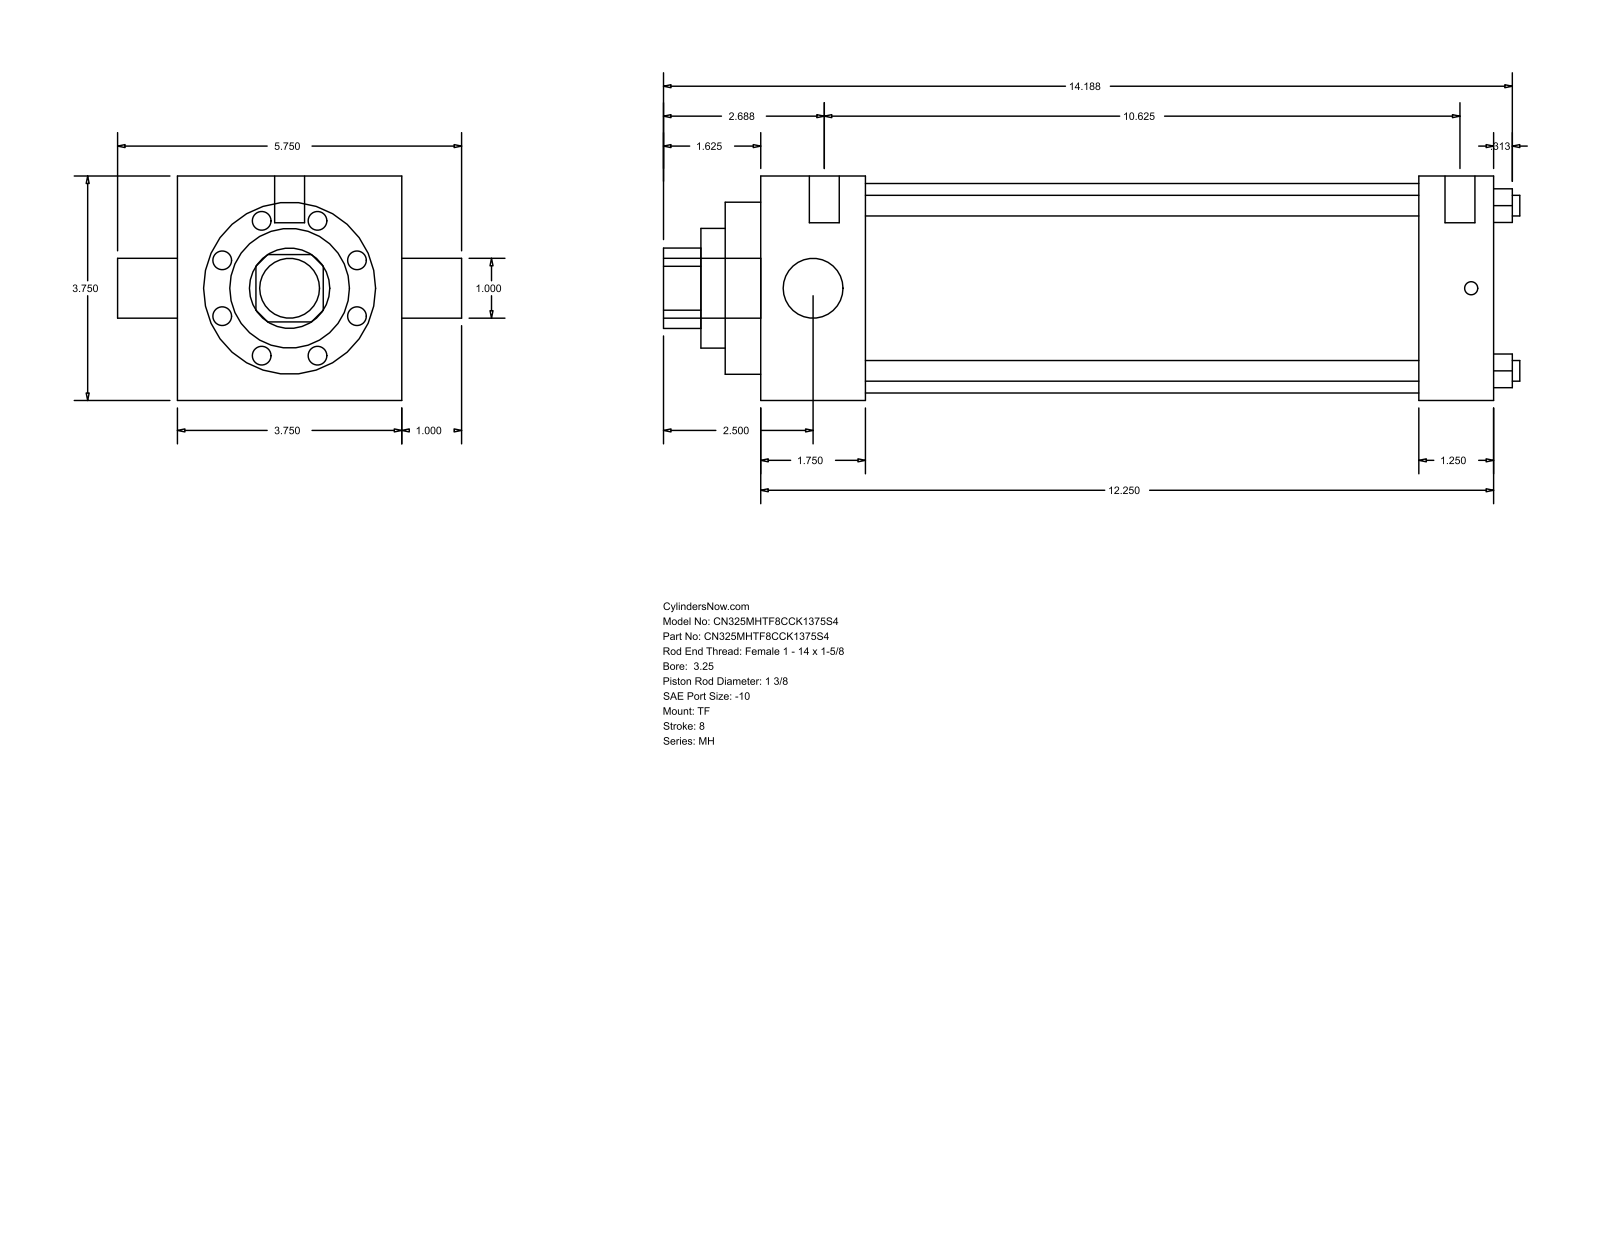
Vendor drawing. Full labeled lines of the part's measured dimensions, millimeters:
Part name (STEP PRODUCT): MH_TF__0325_1.375
STEP written by: GSSL Pune (CONFIG_CONTROL_DESIGN)
Units: millimetres
Bodies: 0 solids, 86 faces (61 planar, 25 cylindrical, 0 other)
Overall size (bounding box): 363.54 × 146.05 × 95.25
Round holes (diameter × count): ⌀8.76 ×4, ⌀25.4 ×1, ⌀34.92 ×1, ⌀50.8 ×1, ⌀73.03 ×1, ⌀88.9 ×1
Round bosses / shafts (diameter × count): ⌀5.56 ×3, ⌀12.7 ×2, ⌀25.4 ×1
Partial cylindrical surfaces — rounded edges, fillets, slot ends (radius × count): R17.06 ×1
Main face-to-face distances: 95.24, 311.16, 44.45, 279.41, 234.96, 266.71, 31.75, 15.08, 59.53, 294.49
Hole centre spacings: 49.57, 70.1, 99.14
